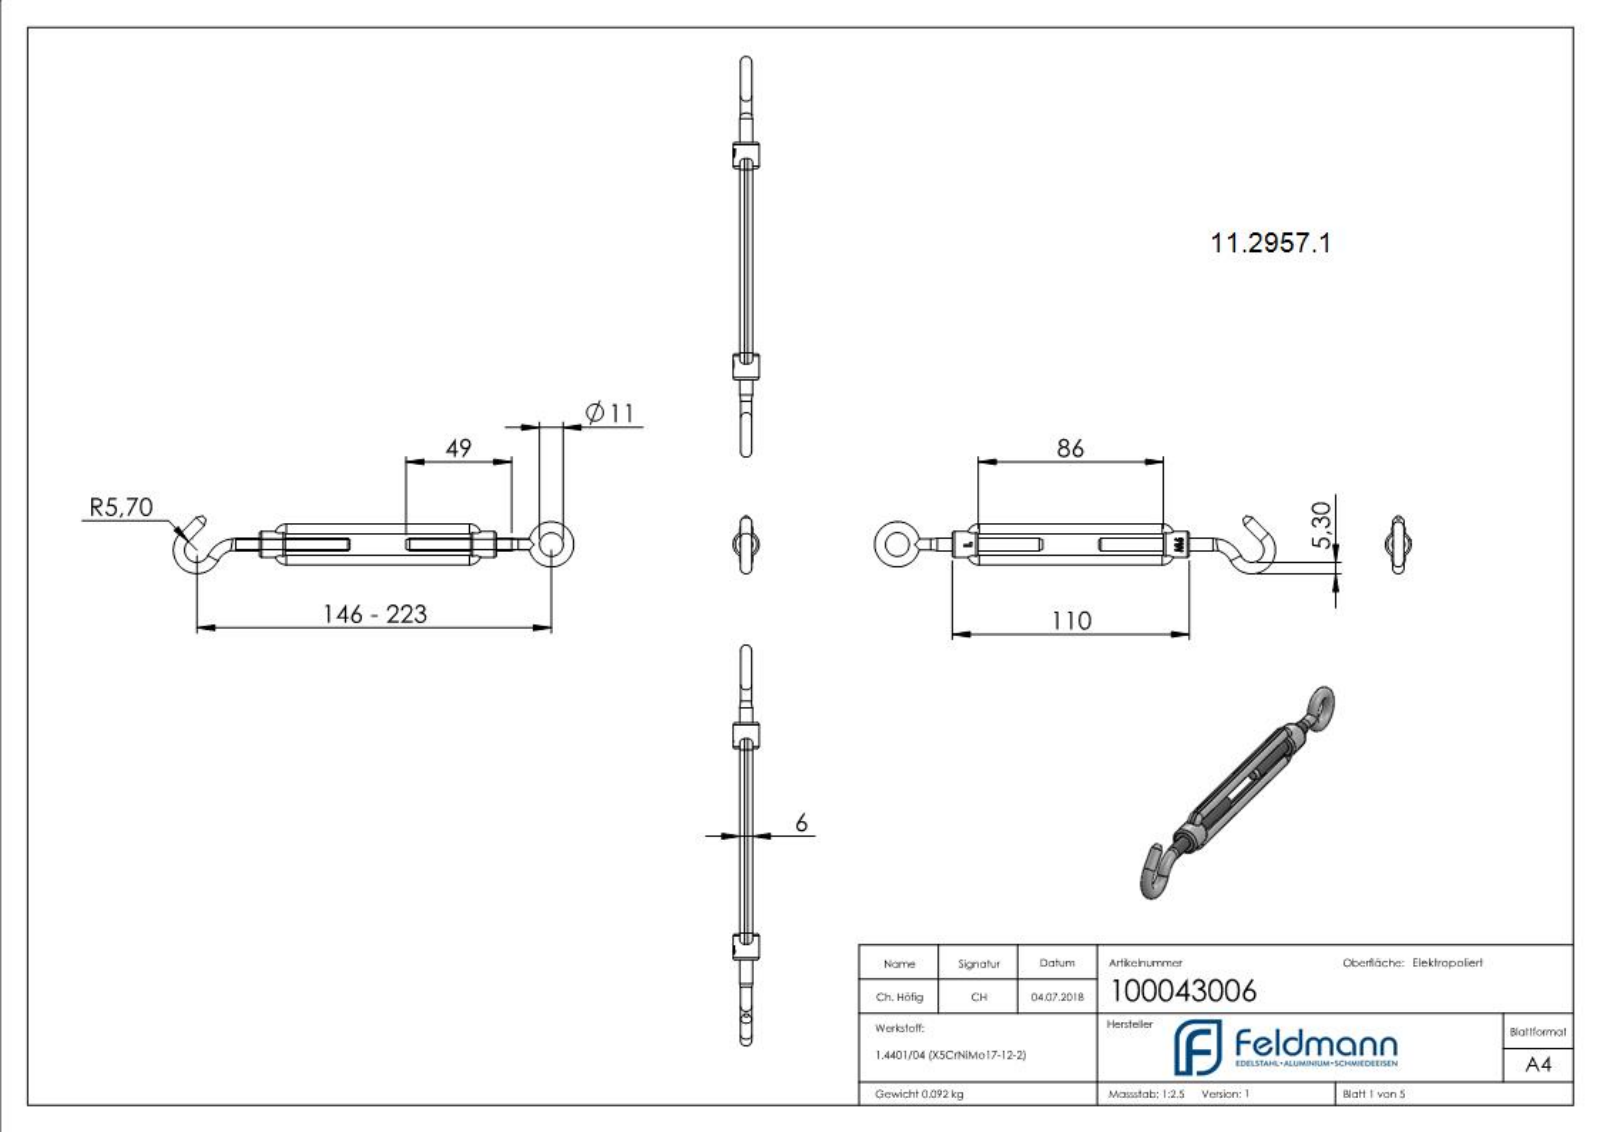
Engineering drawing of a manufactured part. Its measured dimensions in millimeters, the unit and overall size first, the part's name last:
Units: millimetres
Overall size (bounding box): 186 × 26.94 × 12
Round holes (diameter × count): ⌀5 ×1
Round bosses / shafts (diameter × count): ⌀12 ×1, ⌀6 ×1, ⌀5.3 ×1
Partial cylindrical surfaces — rounded edges, fillets, slot ends (radius × count): R1 ×4, R2.25 ×4, R5.5 ×4, R5.98 ×1
Main face-to-face distances: 4.5, 14.5, 19, 10, 98, 12, 110, 86, 42, 68
Volume: 11 561 mm³ · Surface area: 8 401 mm²
Bodies: 3 solids, 121 faces (22 planar, 34 cylindrical, 65 other)
Part name (STEP PRODUCT): 10004300X Teil3_100043006 Teil3; 10004300X Teil2_100043006 Teil2; 100043006; 10004300X Teil1_100043006 Teil1
STEP written by: SolidWorks 2015 (CONFIG_CONTROL_DESIGN)
